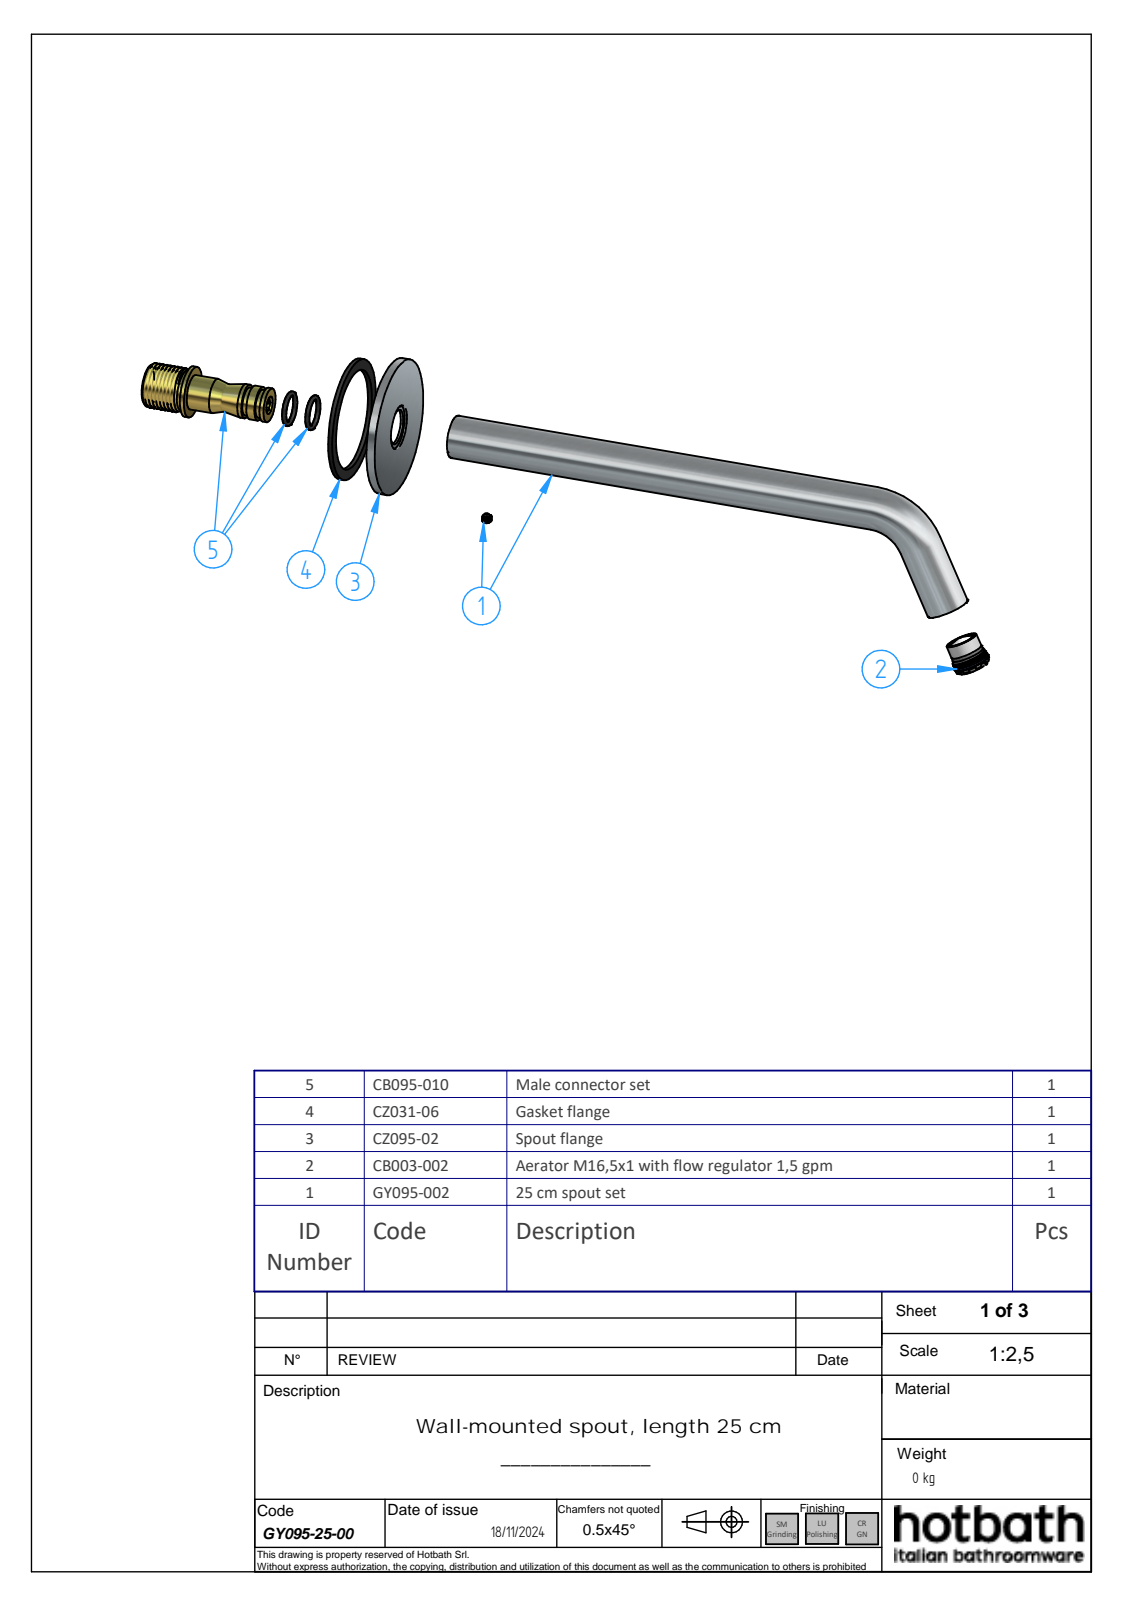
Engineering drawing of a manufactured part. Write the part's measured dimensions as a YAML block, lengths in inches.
part_name: "GY095-25-00; CZ095-02; GY095-002; GY095-02 (+3 more)"
step_written_by: "Solid Edge (AUTOMOTIVE_DESIGN)"
units: inches
bodies: {solids: 4, faces: 136, planar: 64, cylindrical: 30, other: 42}
overall_size: [10.094, 3.161, 2.52]
volume: 2.396
surface_area: 61.03
round_holes:
  - {diameter: 0.63, count: 2}
  - {diameter: 0.128, count: 1}
  - {diameter: 0.157, count: 1}
  - {diameter: 0.48, count: 1}
  - {diameter: 0.574, count: 1}
  - {diameter: 0.634, count: 1}
  - {diameter: 0.642, count: 1}
  - {diameter: 0.659, count: 1}
  - {diameter: 0.807, count: 1}
  - {diameter: 0.984, count: 1}
  - {diameter: 2.382, count: 1}
round_bosses_or_shafts:
  - {diameter: 0.787, count: 2}
  - {diameter: 2.52, count: 1}
  - {diameter: 1.142, count: 1}
  - {diameter: 0.65, count: 1}
  - {diameter: 0.607, count: 1}
  - {diameter: 0.6, count: 1}
  - {diameter: 0.599, count: 1}
  - {diameter: 0.592, count: 1}
face_to_face_distances: [0.091, 0.087, 0.157, 0.067, 0.039, 0.071, 0.031, 0.035, 0.126, 0.118]
